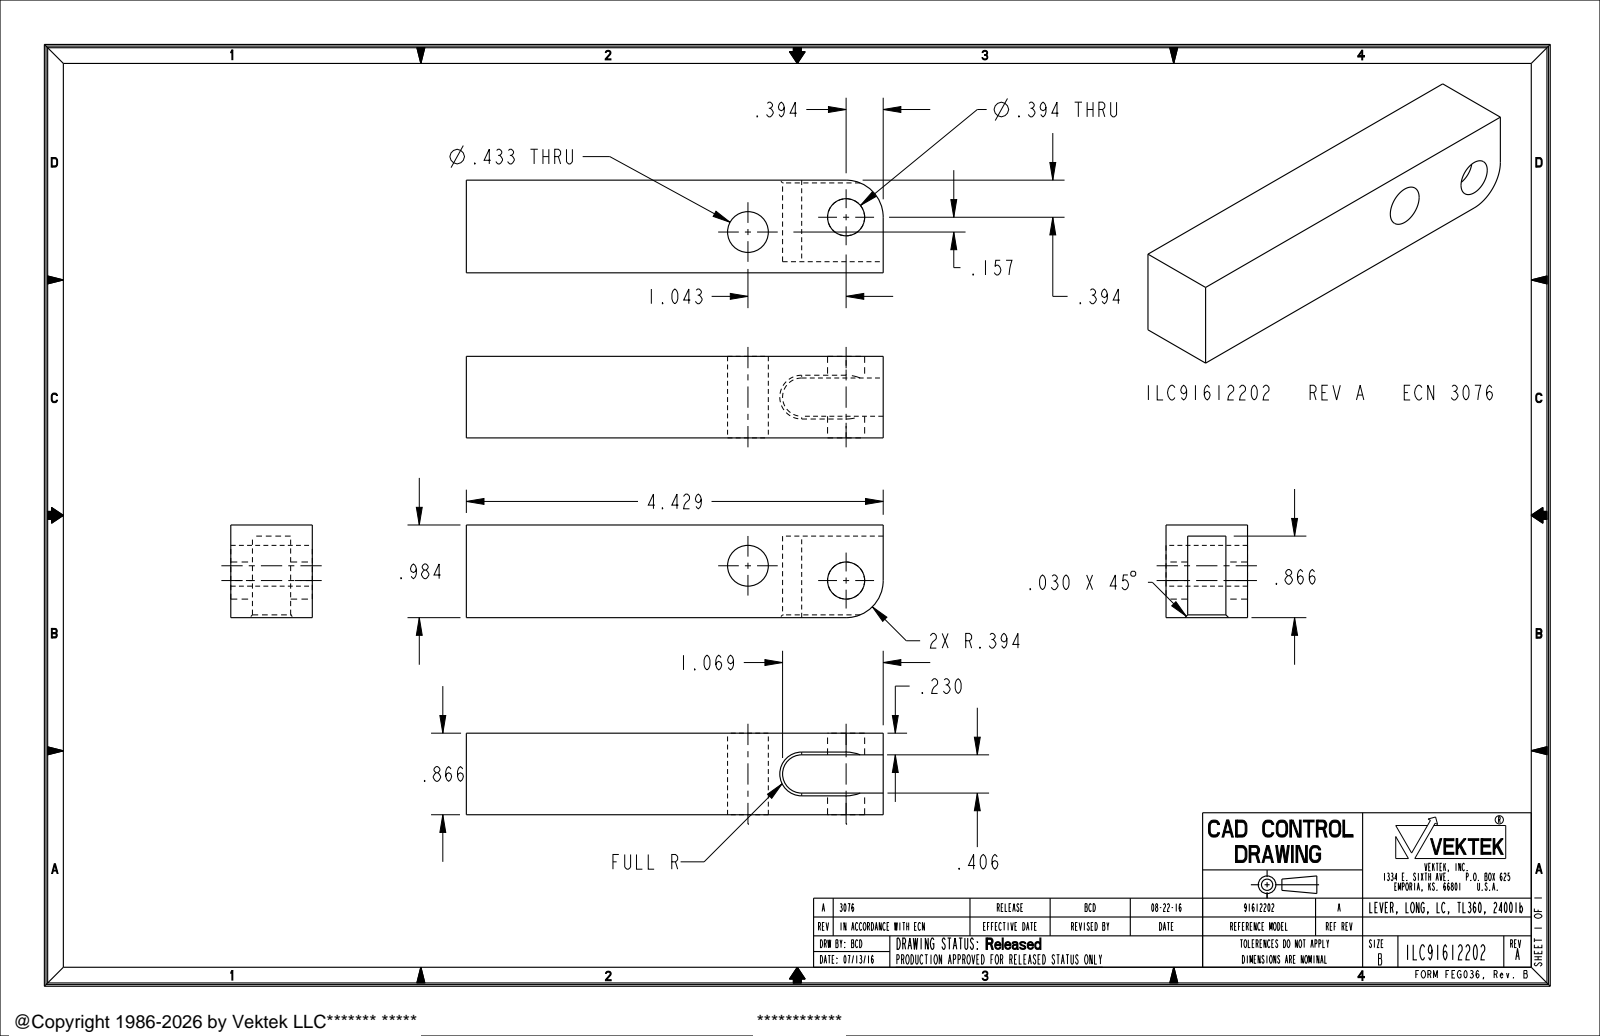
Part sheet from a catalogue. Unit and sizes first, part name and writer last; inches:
Units: inches
Overall size (bounding box): 4.429 × 0.984 × 0.866
Round holes (diameter × count): ⌀0.394 ×1, ⌀0.433 ×1
Partial cylindrical surfaces — rounded edges, fillets, slot ends (radius × count): R0.203 ×1, R0.394 ×1
Main face-to-face distances: 0.866, 0.984, 0.23, 0.636, 0.406, 0.118, 4.429
Hole centre spacings: 1.055
Volume: 3.214 in³ · Surface area: 20.52 in²
Bodies: 1 solid, 21 faces (11 planar, 9 cylindrical, 1 other)
Part name (STEP PRODUCT): ILC91612202
STEP written by: PRO/ENGINEER BY PARAMETRIC TECHNOLOGY CORPORATION, 2013320 (AUTOMOTIVE_DESIGN)
